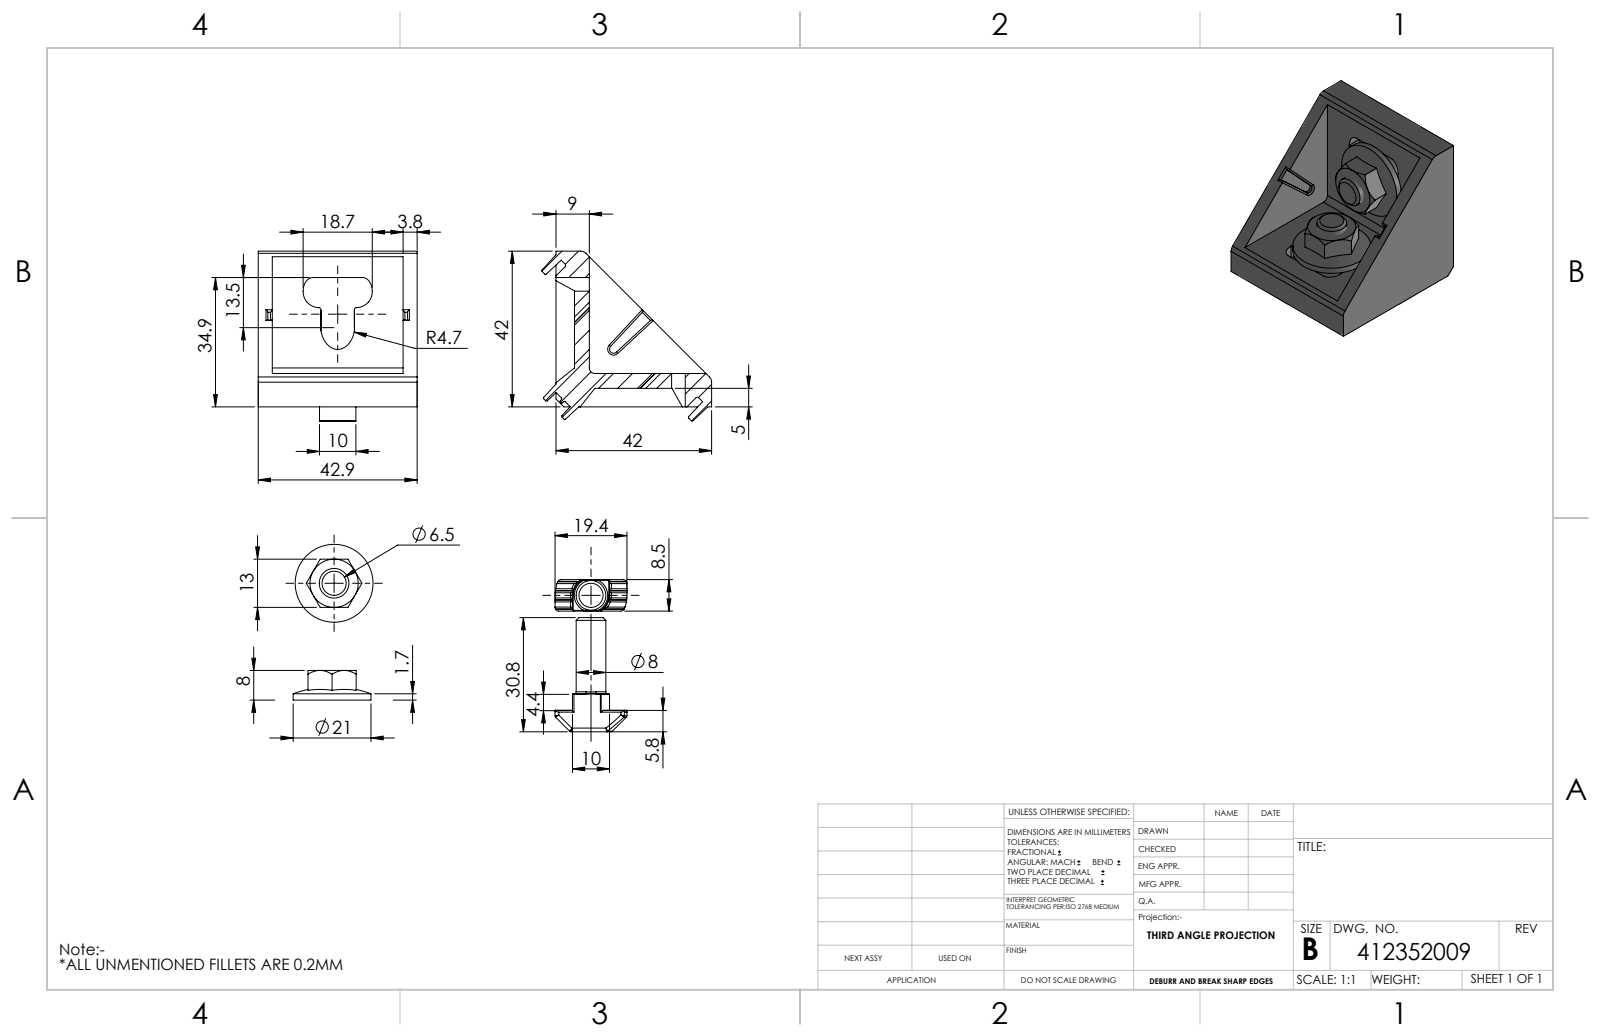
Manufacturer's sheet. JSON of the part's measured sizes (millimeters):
{"part_name": "412352009 Winkel 43x42 Set; 412348526 Winkel 43x42; 412528718 Hammerschraube M8x25 N10; 412345081 Bundmutter M8", "step_written_by": "Autodesk Inventor 2019 (AUTOMOTIVE_DESIGN)", "units": "millimeters", "bodies": {"solids": 5, "faces": 454, "planar": 187, "cylindrical": 153, "other": 114}, "overall_size": [53.8, 53.8, 42.88], "volume_mm3": 28847, "surface_area_mm2": 17049, "round_holes": [[6.65, 2]], "round_bosses_or_shafts": [[21, 2], [8, 2]], "partial_cylinders_radius": [[1, 38], [0.5, 26], [0.1, 8], [0.2, 8], [0.3, 8], [0.4, 8], [0.25, 4], [2.6, 4]], "face_to_face_distances": [9, 42.88, 3.79, 39.09, 5, 4, 33, 37, 42, 3.39]}
